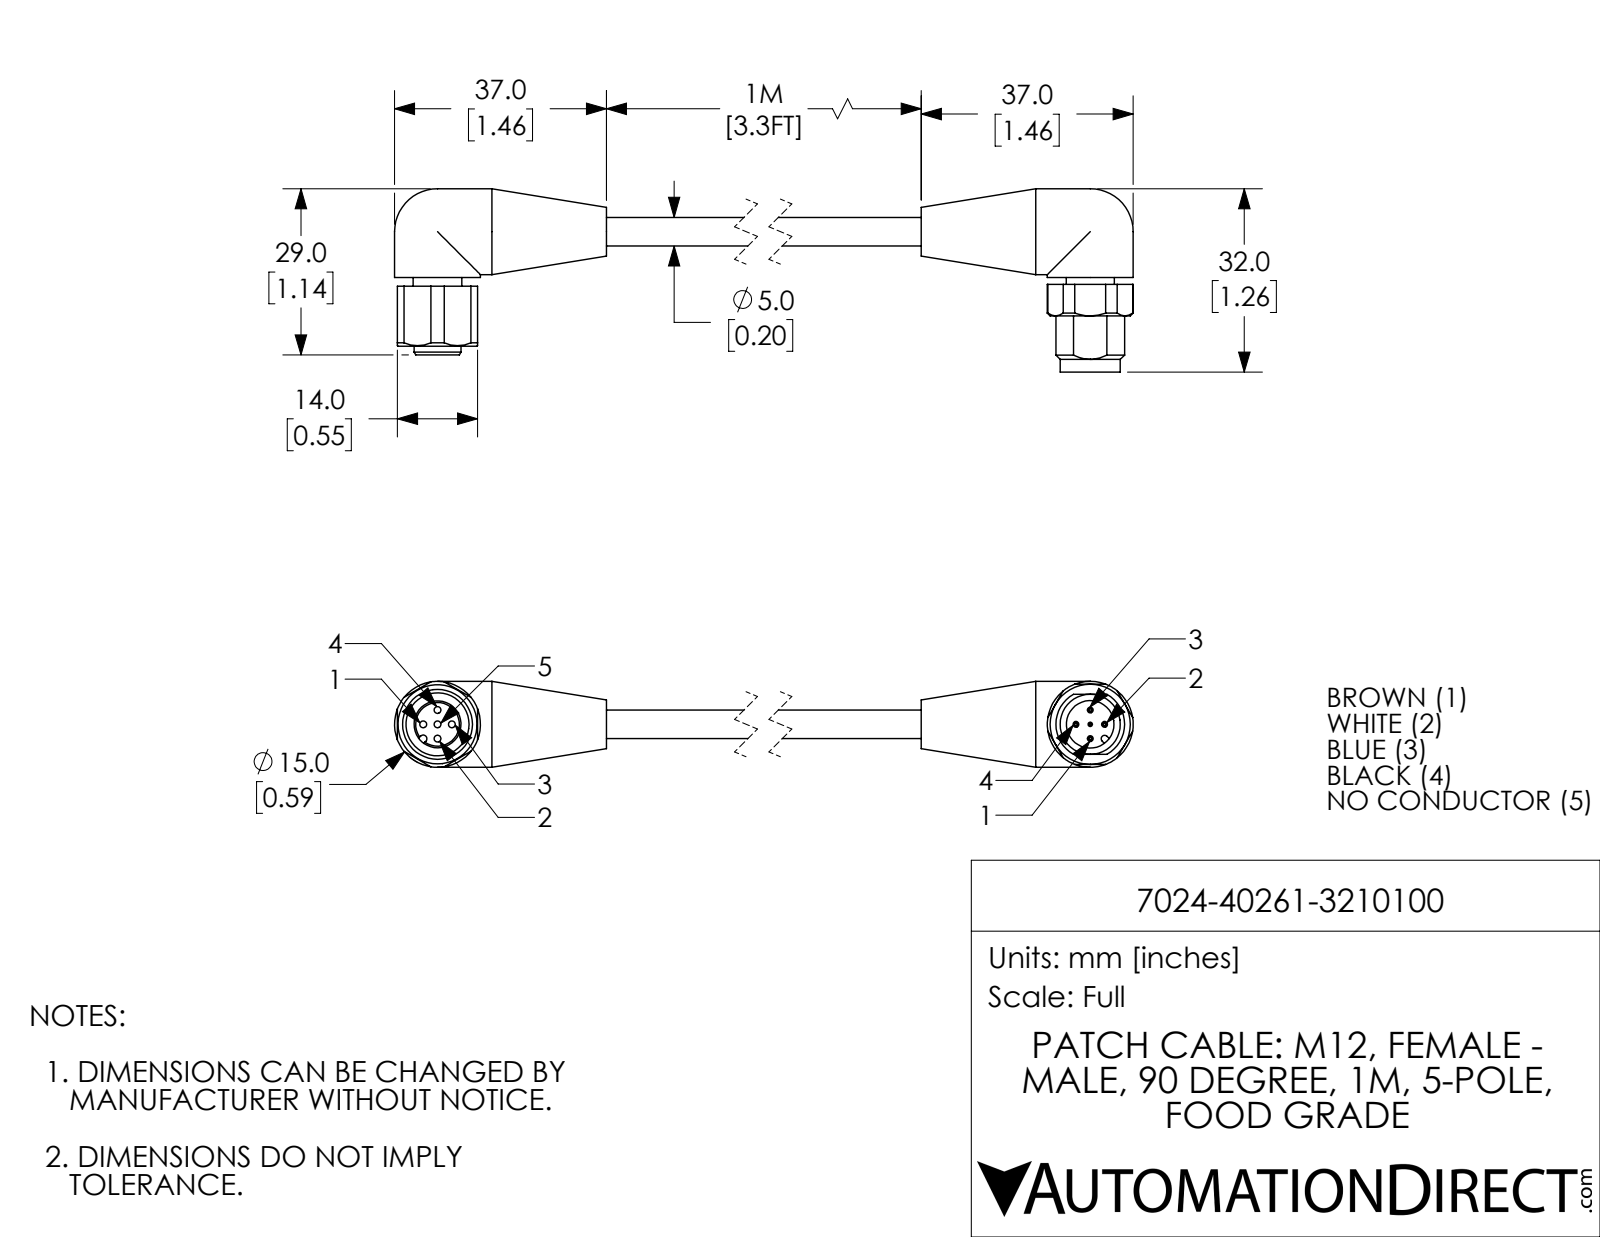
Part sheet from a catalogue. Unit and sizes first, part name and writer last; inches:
Units: inches
Overall size (bounding box): 5.776 × 1.26 × 0.591
Round holes (diameter × count): ⌀0.047 ×5, ⌀0.327 ×1, ⌀0.433 ×1
Round bosses / shafts (diameter × count): ⌀0.039 ×4, ⌀0.591 ×3, ⌀0.413 ×1, ⌀0.335 ×1, ⌀0.331 ×1, ⌀0.323 ×1, ⌀0.197 ×1
Partial cylindrical surfaces — rounded edges, fillets, slot ends (radius × count): R0.024 ×1, R0.026 ×1, R0.236 ×1
Main face-to-face distances: 0.551, 0.059, 0.047, 0.472, 0.413, 0.177, 0.118, 0.069, 0.482, 0.217
Hole centre spacings: 0.098, 0.139, 0.197, 5.186, 5.087, 5.185, 5.283
Volume: 0.892 in³ · Surface area: 10.83 in²
Bodies: 2 solids, 135 faces (43 planar, 61 cylindrical, 31 other)
Part name (STEP PRODUCT): 7024-40261-3210100_FEMALE; 7024-40261-3210100; 7024-40261-3210100_MALE
STEP written by: SolidWorks 2018 (AUTOMOTIVE_DESIGN)
